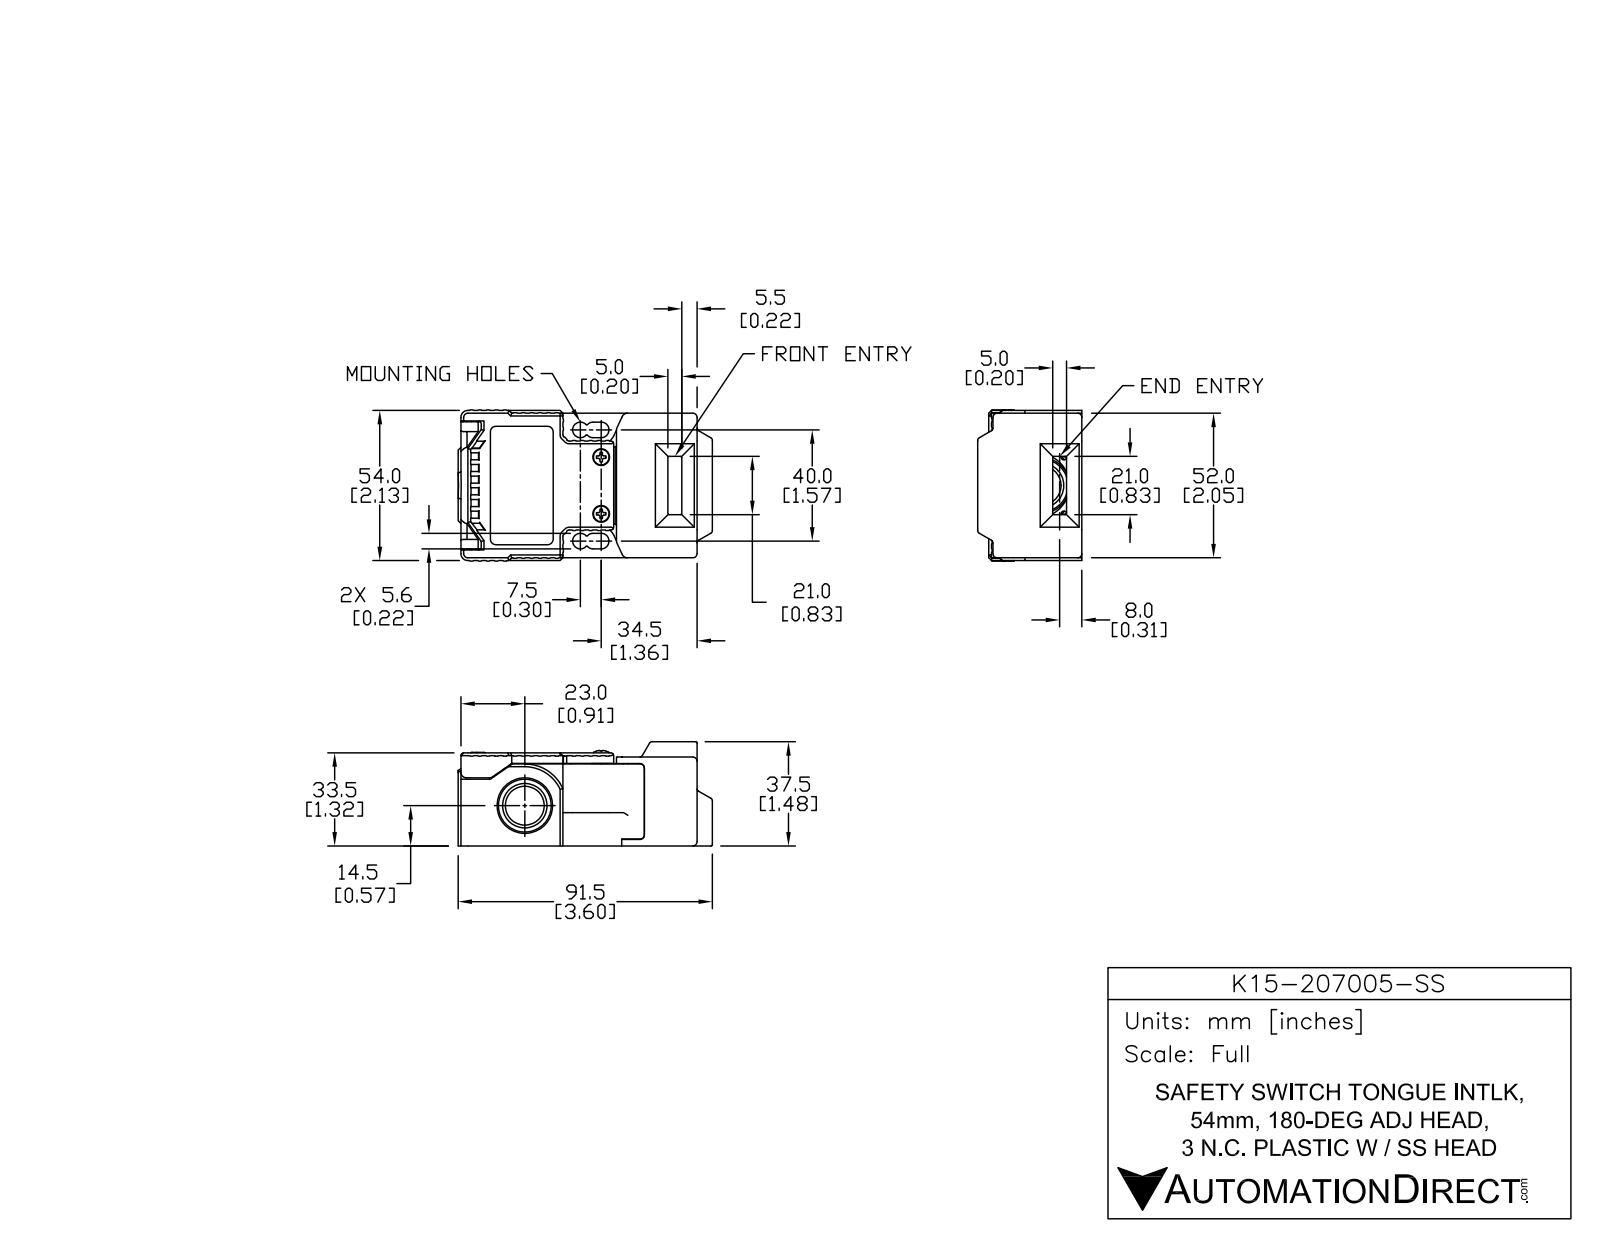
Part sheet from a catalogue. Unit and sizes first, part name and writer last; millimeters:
Units: millimetres
Overall size (bounding box): 91.5 × 58 × 37.5
Round holes (diameter × count): ⌀19.33 ×1, ⌀20 ×1
Round bosses / shafts (diameter × count): ⌀5.6 ×2
Partial cylindrical surfaces — rounded edges, fillets, slot ends (radius × count): R0.5 ×55, R2.8 ×6, R2 ×4, R3 ×4, R4 ×3
Main face-to-face distances: 3, 55, 33.5, 52, 32, 1.5, 85, 5.5, 33.45, 1.45
Volume: 139 541 mm³ · Surface area: 23 526 mm²
Bodies: 1 solid, 308 faces (162 planar, 91 cylindrical, 55 other)
Part name (STEP PRODUCT): K-15-207005-SS
STEP written by: SolidWorks 2013 (AUTOMOTIVE_DESIGN)
